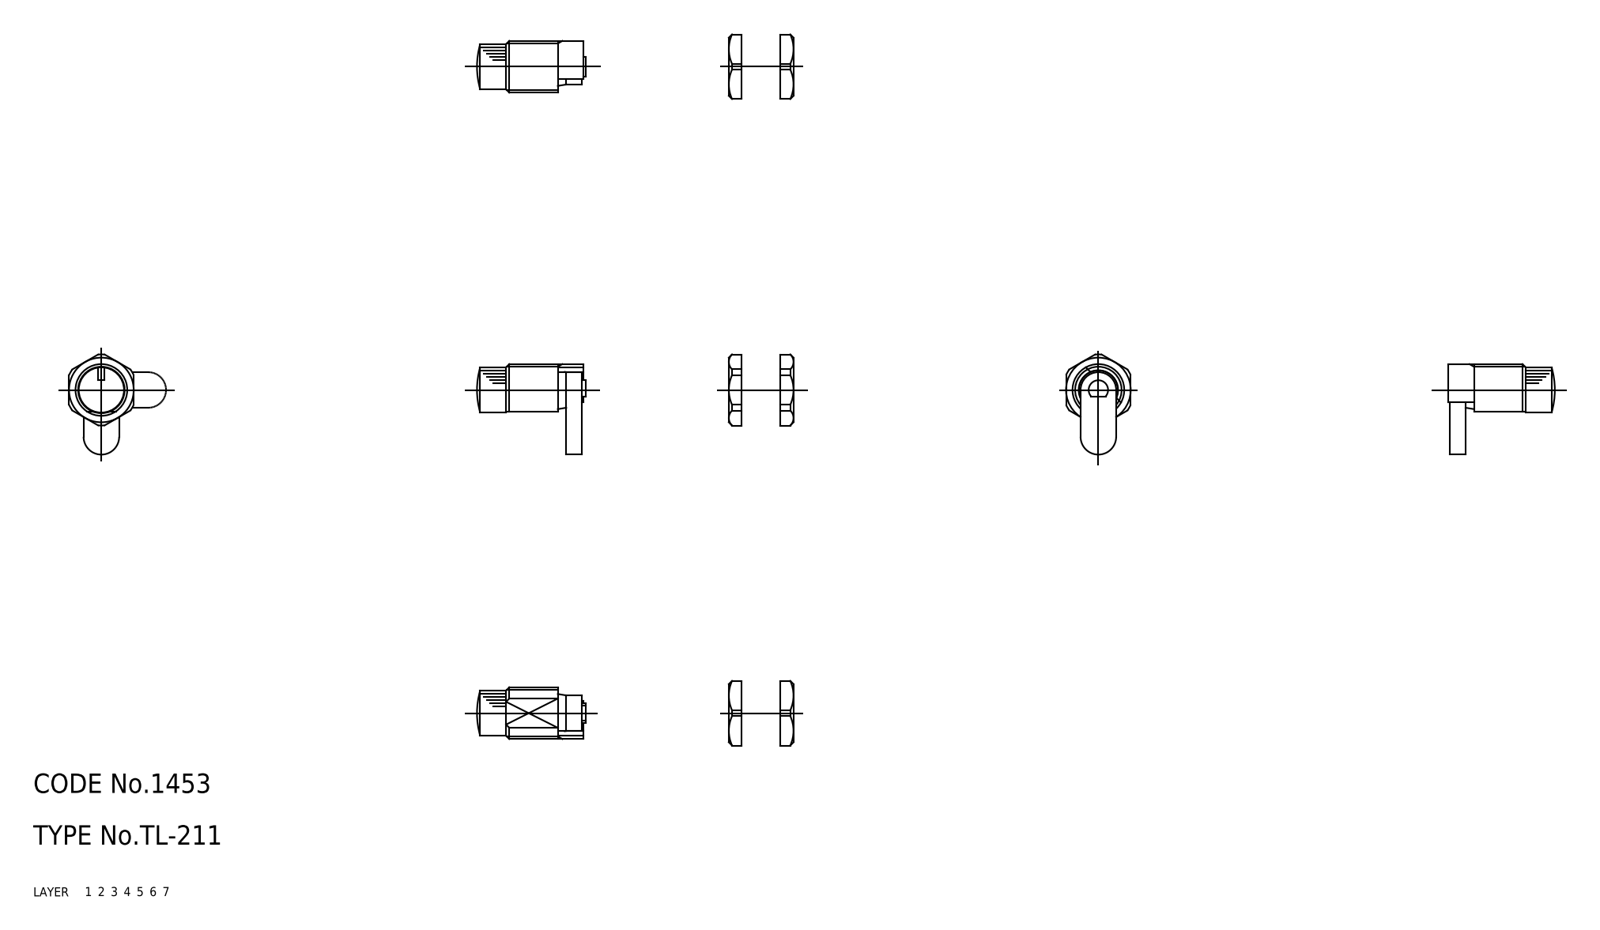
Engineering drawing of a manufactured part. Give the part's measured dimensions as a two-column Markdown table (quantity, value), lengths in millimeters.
| quantity | value |
| --- | --- |
| part name | nut_mr; nut; knob; collar (+2 more) |
| STEP written by | CADfix (AUTOMOTIVE_DESIGN) |
| units | millimeters |
| bodies | 6 solids, 78 faces (0 planar, 0 cylindrical, 78 other) |
| overall size | 16.8 × 15.5 × 10 |
| volume | 824 mm³ |
| surface area | 1 498 mm² |
